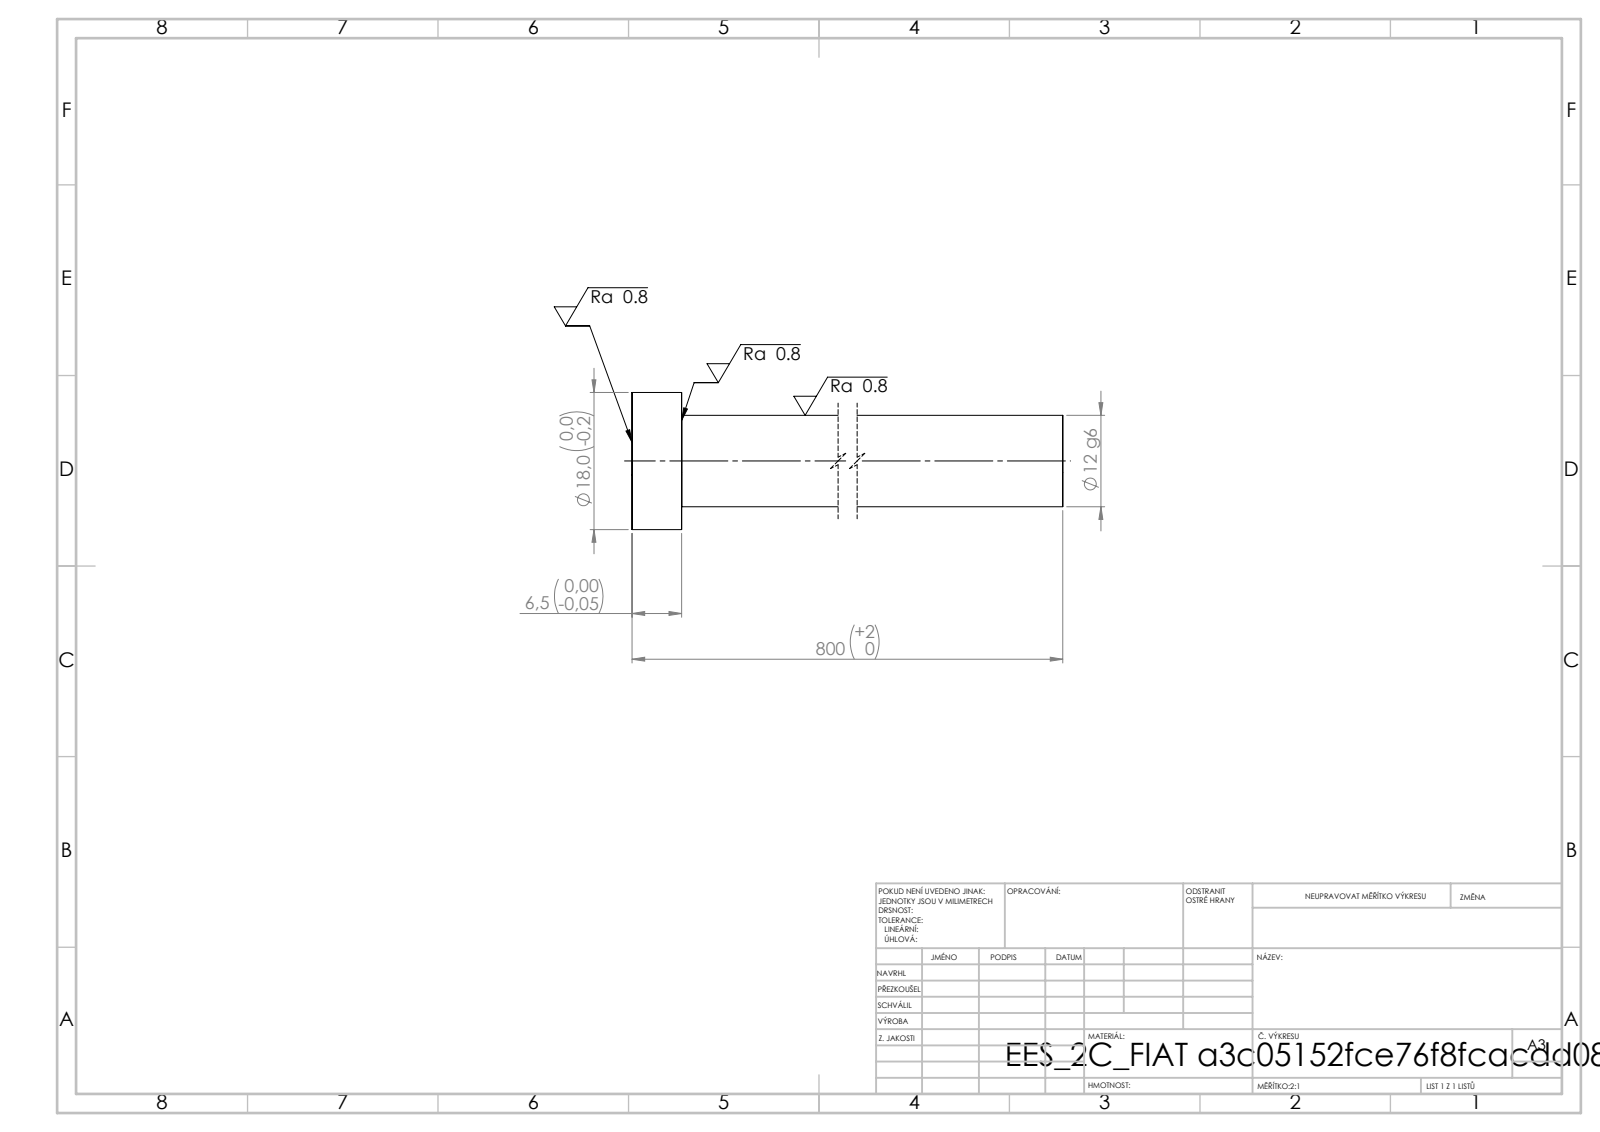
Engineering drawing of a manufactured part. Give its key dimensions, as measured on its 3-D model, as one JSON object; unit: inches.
{"step_written_by": "SolidWorks 2019 (CONFIG_CONTROL_DESIGN)", "units": "inches", "bodies": {"solids": 1, "faces": 7, "planar": 3, "cylindrical": 4, "other": 0}, "overall_size": [31.496, 0.709, 0.709], "volume_in3": 5.577, "surface_area_in2": 47.73, "round_bosses_or_shafts": [[0.709, 1], [0.472, 1]], "face_to_face_distances": [0.256, 31.496, 31.24]}
